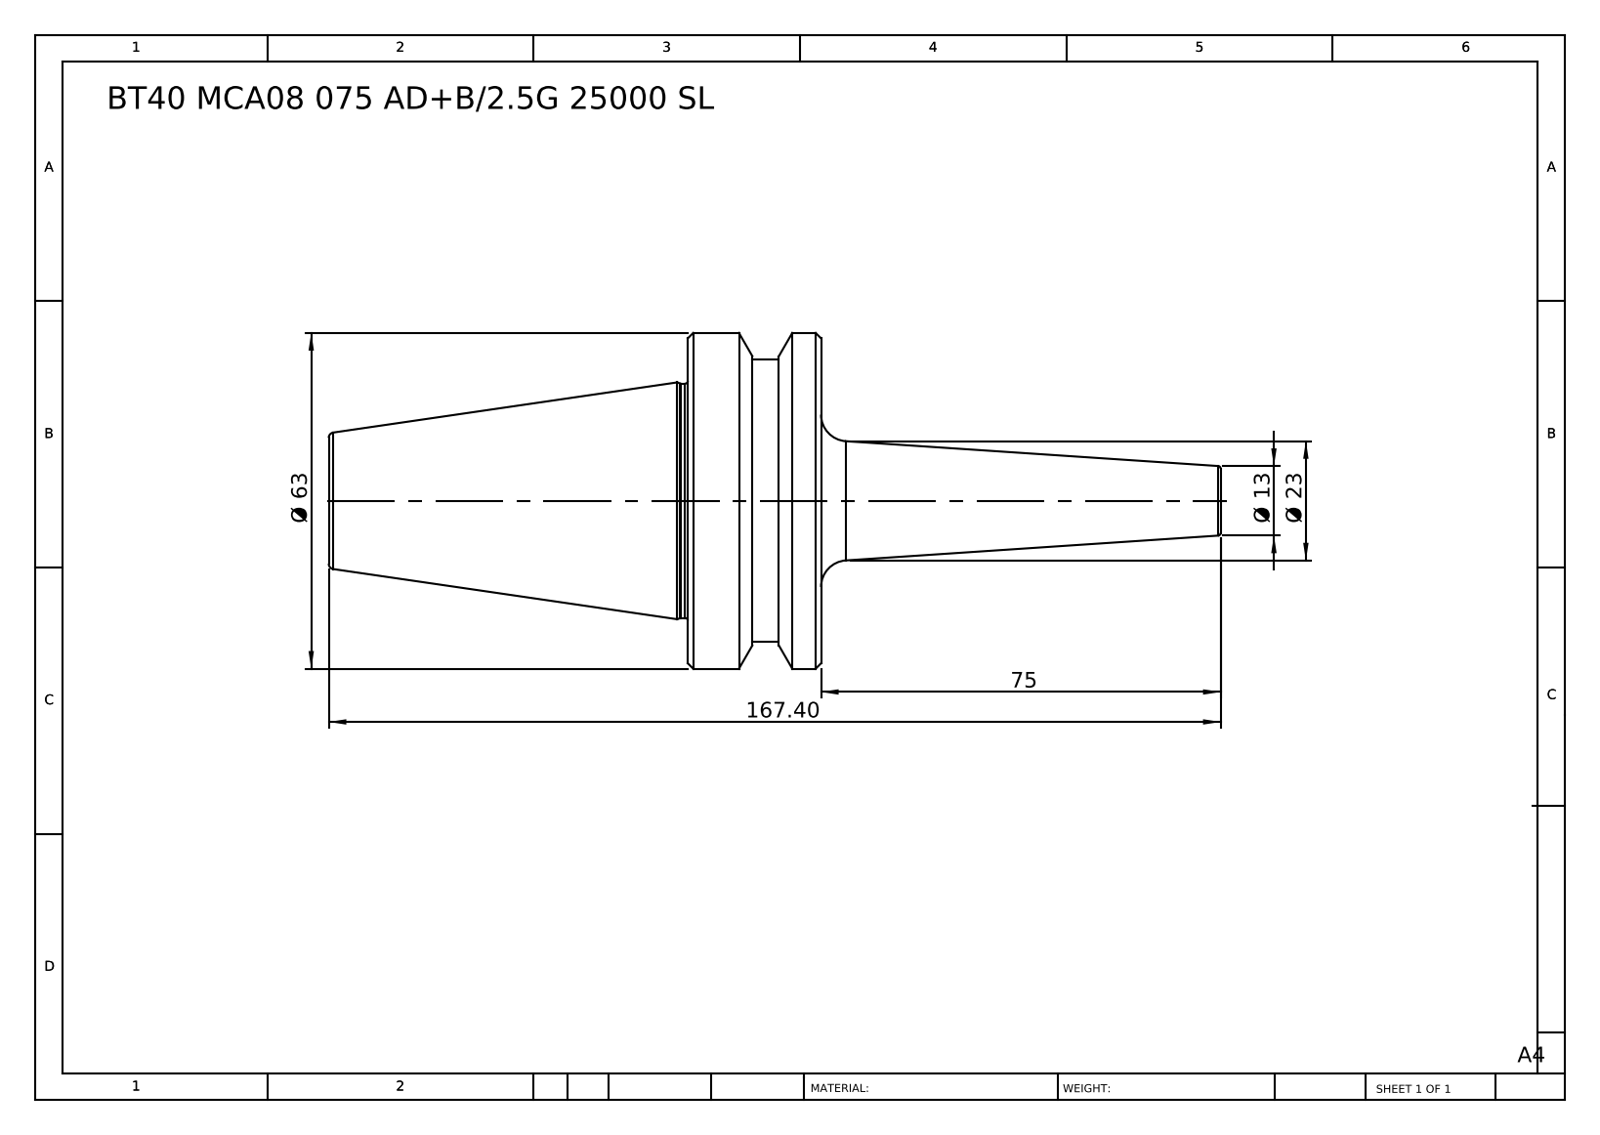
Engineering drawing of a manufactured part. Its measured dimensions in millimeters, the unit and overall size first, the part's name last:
Units: millimetres
Overall size (bounding box): 167.4 × 63 × 63
Round bosses / shafts (diameter × count): ⌀63 ×1, ⌀53 ×1, ⌀44 ×1
Main face-to-face distances: 25, 92.4, 67.4, 75, 100, 167.4, 87.9, 12.9, 12.1, 79.5
Volume: 158 280 mm³ · Surface area: 22 171 mm²
Bodies: 1 solid, 38 faces (6 planar, 8 cylindrical, 24 other)
Part name (STEP PRODUCT): BT40 MCA08 075 AD+B-2.5G 25000 SL
STEP written by: SolidWorks 2014 (CONFIG_CONTROL_DESIGN)
